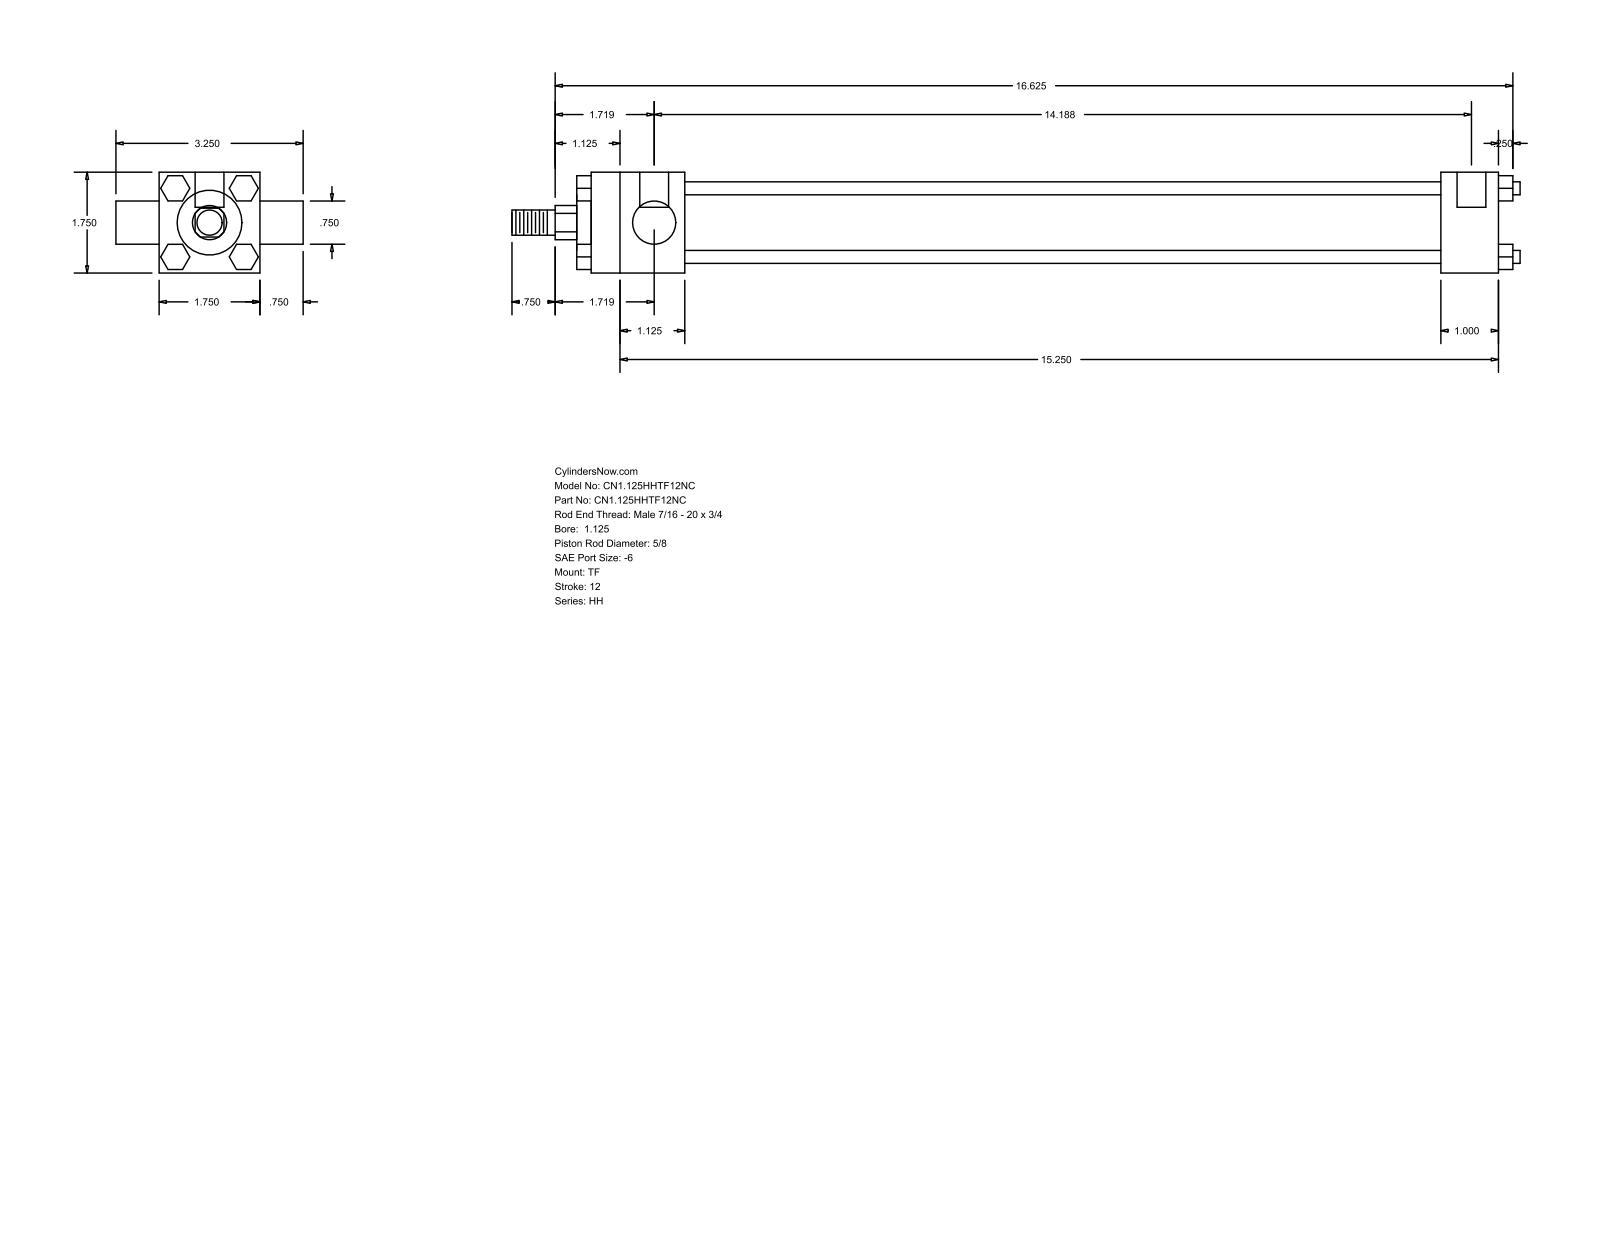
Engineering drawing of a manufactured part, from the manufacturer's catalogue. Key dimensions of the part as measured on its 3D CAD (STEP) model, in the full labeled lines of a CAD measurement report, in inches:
Part name (STEP PRODUCT): HH_TF__0112_0.625
STEP written by: GSSL Pune (CONFIG_CONTROL_DESIGN)
Units: inches
Bodies: 0 solids, 120 faces (92 planar, 28 cylindrical, 0 other)
Overall size (bounding box): 17.5 × 3.25 × 1.75
Round holes (diameter × count): ⌀0.219 ×3, ⌀0.5 ×2
Round bosses / shafts (diameter × count): ⌀0.225 ×4, ⌀1.375 ×1, ⌀1.125 ×1, ⌀0.75 ×1, ⌀0.625 ×1, ⌀0.437 ×1
Partial cylindrical surfaces — rounded edges, fillets, slot ends (radius × count): R0.297 ×1
Main face-to-face distances: 1.75, 0.437, 13.125, 14.125, 1, 1.625, 14.75, 15.75, 1.875, 0.25
Hole centre spacings: 0.125, 14.063, 14.187
